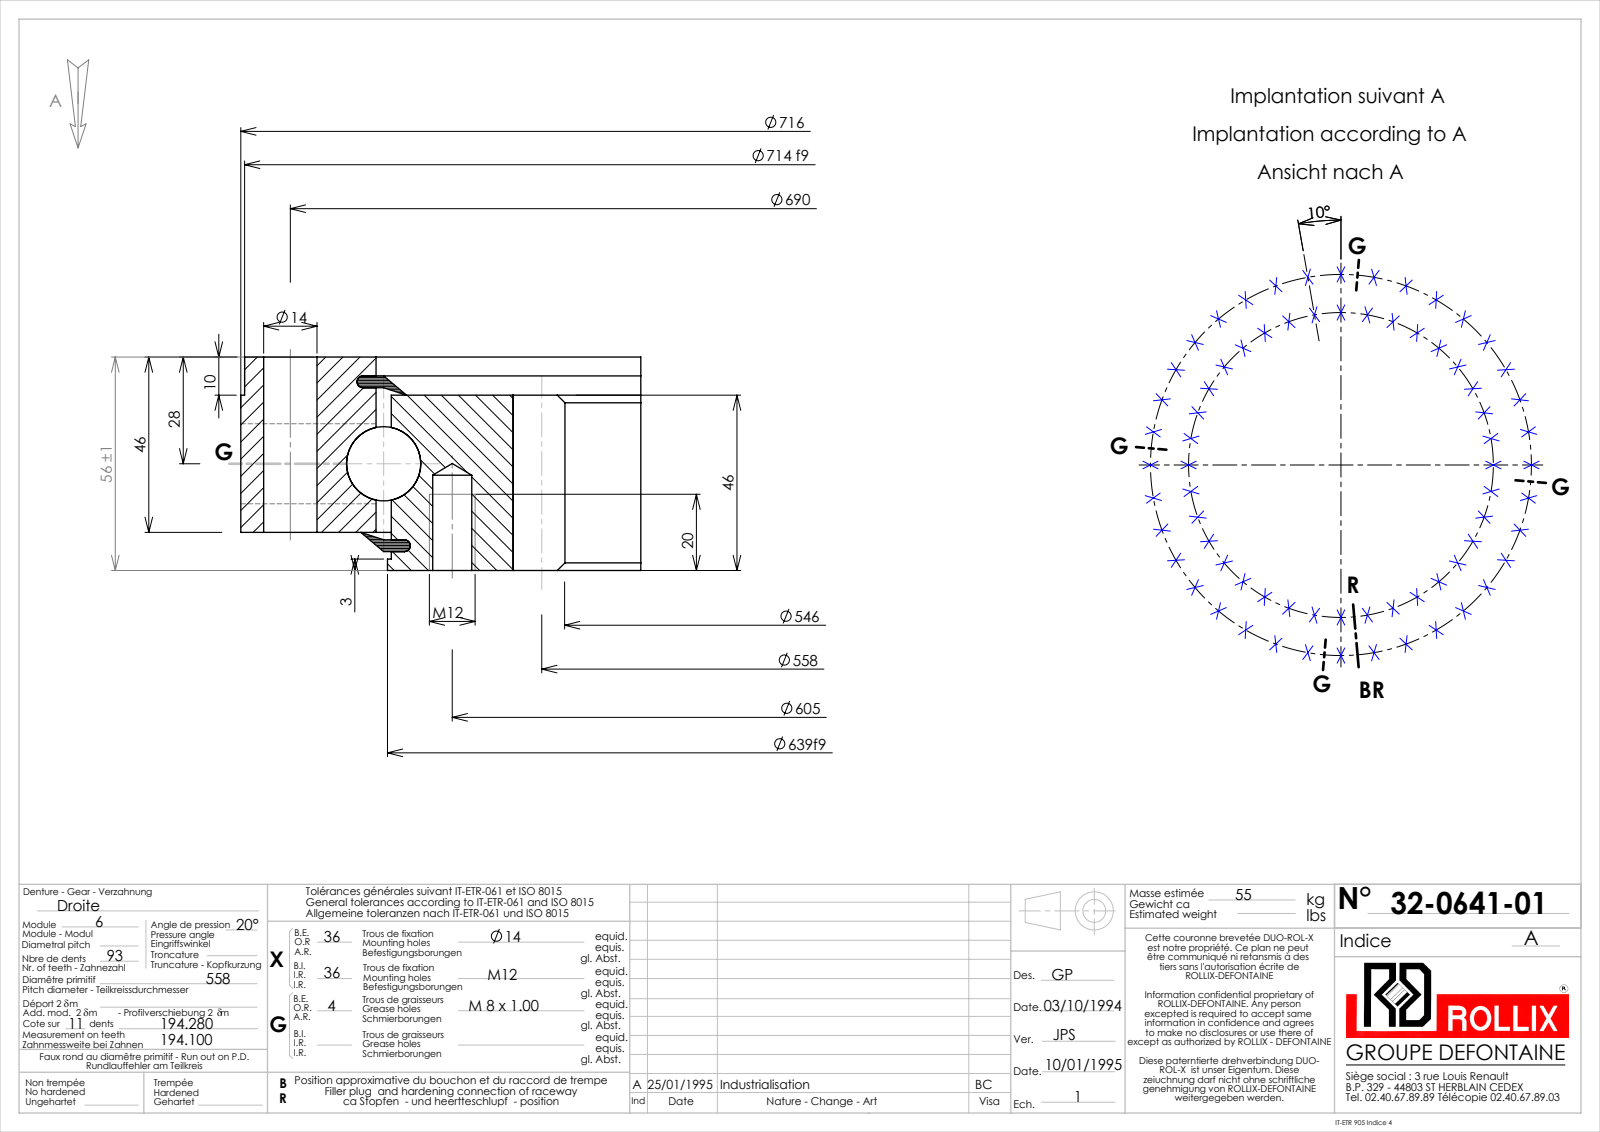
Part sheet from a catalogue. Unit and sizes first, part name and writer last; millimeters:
Units: millimetres
Overall size (bounding box): 732.81 × 732.81 × 56
Round holes (diameter × count): ⌀10.25 ×36, ⌀14 ×36, ⌀7 ×4, ⌀645 ×1
Round bosses / shafts (diameter × count): ⌀8 ×4, ⌀716 ×1, ⌀714 ×1, ⌀639 ×1, ⌀637 ×1
Partial cylindrical surfaces — rounded edges, fillets, slot ends (radius × count): R273 ×1, R286.5 ×1
Main face-to-face distances: 46, 10, 36, 56, 1.95, 5.05, 43, 8.05, 47.95, 37.95
Hole centre spacings: 105.06, 206.92, 302.5, 568.51, 523.94, 584.38, 602.7, 156.59
Volume: 6 136 000 mm³ · Surface area: 1 032 000 mm²
Bodies: 9 solids, 932 faces (240 planar, 365 cylindrical, 327 other)
Part name (STEP PRODUCT): 32-0641-01
STEP written by: SolidWorks 2016 (CONFIG_CONTROL_DESIGN)
